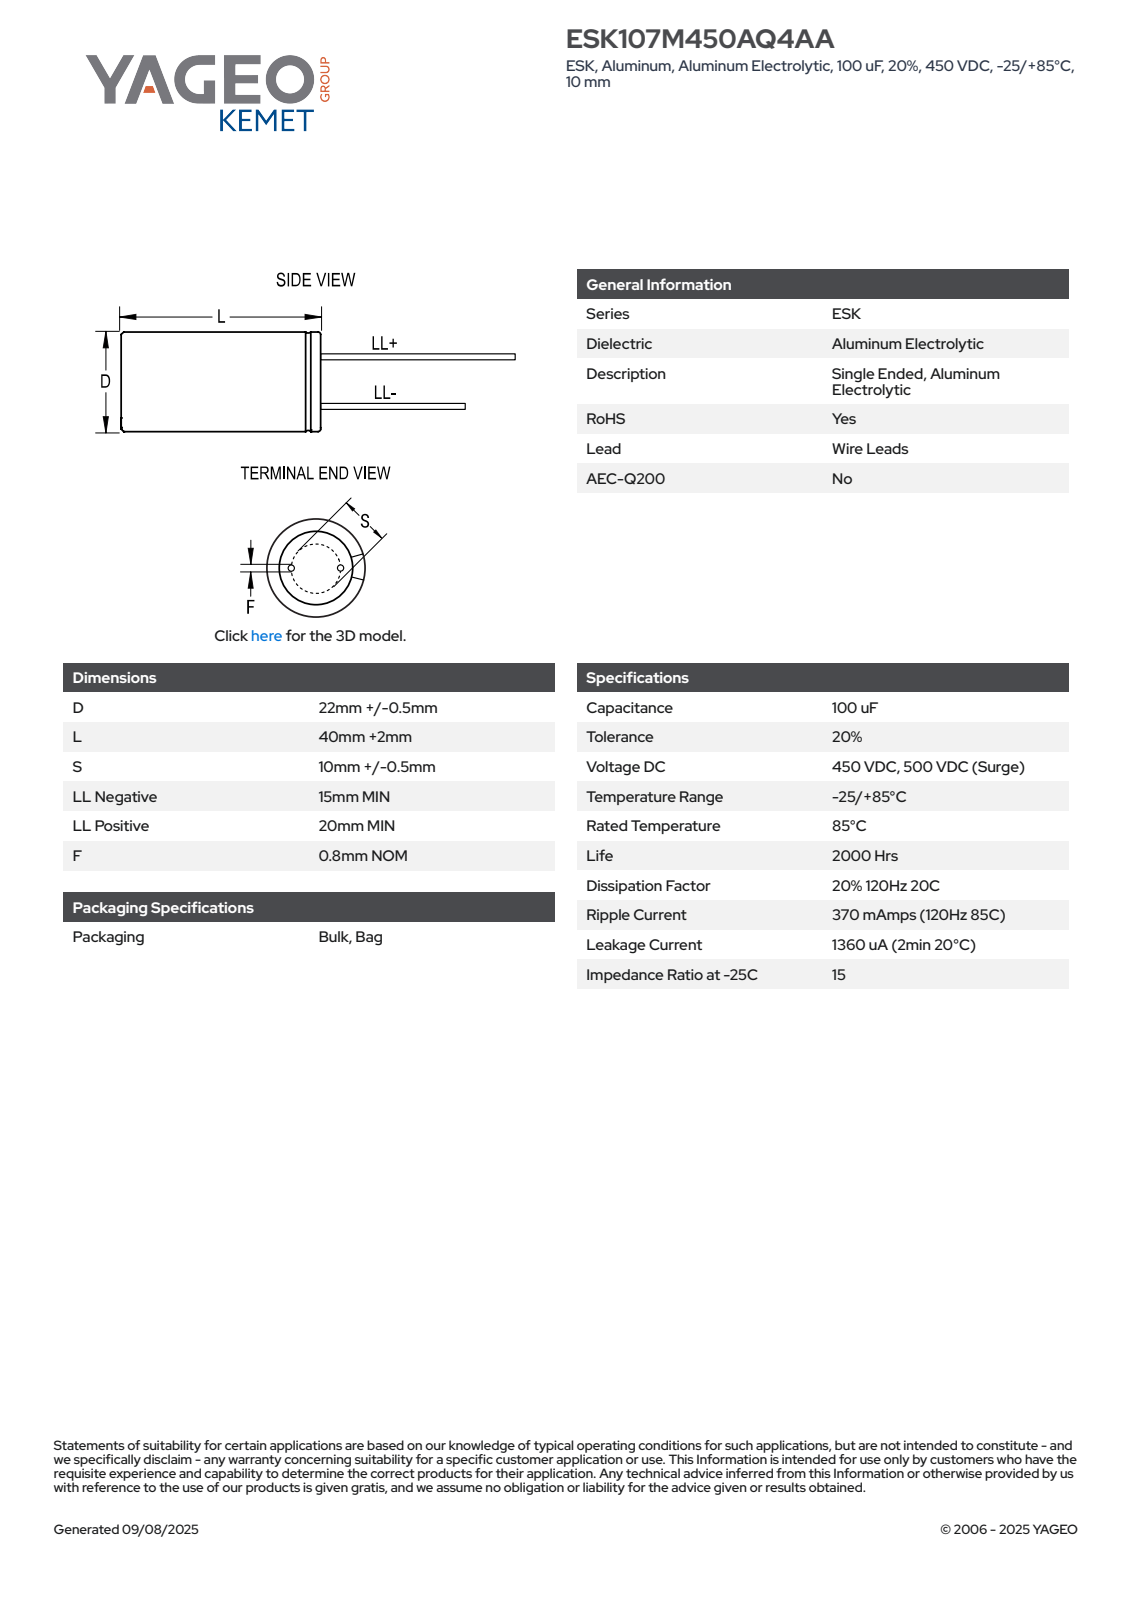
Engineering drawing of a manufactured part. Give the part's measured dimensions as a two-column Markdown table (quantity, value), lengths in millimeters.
| quantity | value |
| --- | --- |
| part name | CAR_KLP_22X40_D22.5L42S10F0.8 |
| STEP written by | SolidWorks 2014 (AUTOMOTIVE_DESIGN) |
| units | millimeters |
| bodies | 4 solids, 75 faces (61 planar, 8 cylindrical, 6 other) |
| overall size | 62.01 × 22.5 × 22.5 |
| volume | 16 599 mm³ |
| surface area | 3 971 mm² |
| round bosses / shafts (diameter × count) | 0.8 × 2, 22.5 × 1 |
| main face-to-face distances | 42, 42.01, 57.01, 62.01, 57, 62, 15, 20, 5, 3.02 |
